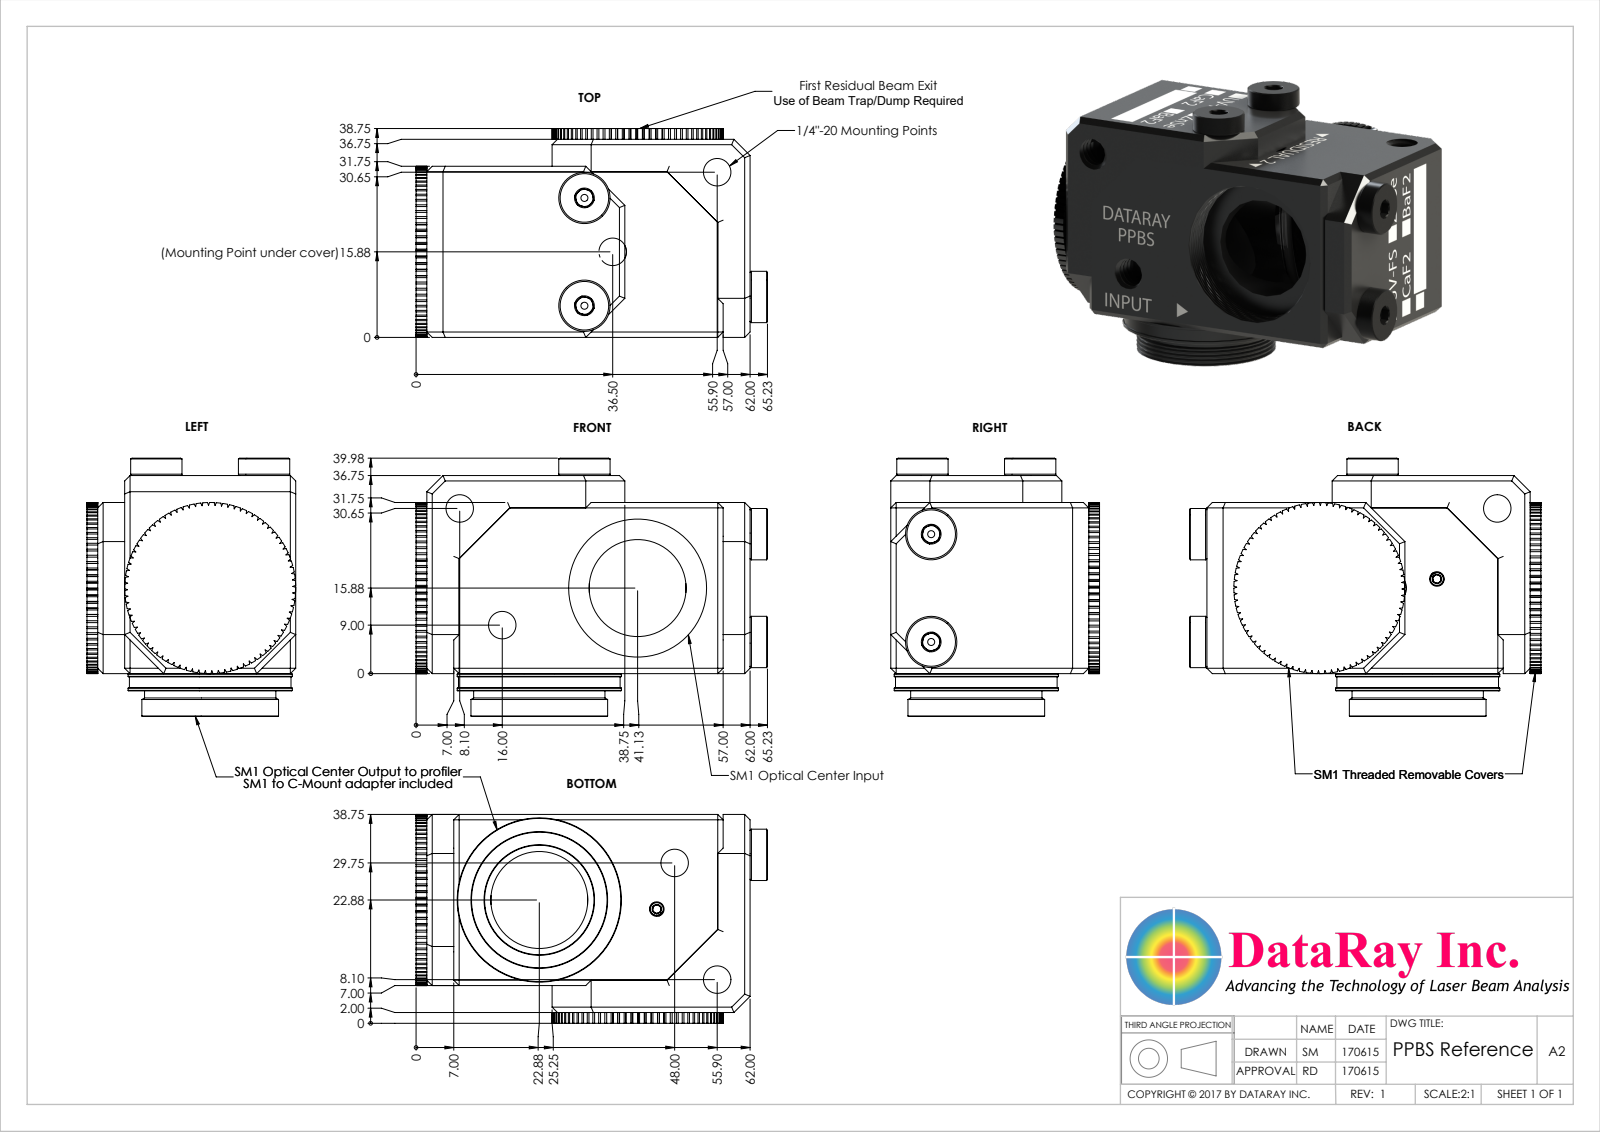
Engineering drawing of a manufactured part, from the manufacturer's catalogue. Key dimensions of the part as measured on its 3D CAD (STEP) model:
Part name (STEP PRODUCT): Adapter-CM(M)-SM1(M); Cap-PPBS; Mount Fastener; Wedge-UV-FS (+4 more)
STEP written by: SolidWorks 2017 (CONFIG_CONTROL_DESIGN)
Units: millimetres
Bodies: 14 solids, 1243 faces (544 planar, 441 cylindrical, 258 other)
Overall size (bounding box): 65.23 × 47.93 × 38.75
Volume: 52 327 mm³ · Surface area: 32 496 mm²
Round holes (diameter × count): ⌀5.11 ×10, ⌀25.4 ×4, ⌀18 ×3, ⌀2.71 ×2, ⌀6.35 ×2, ⌀20 ×2, ⌀25.6 ×2, ⌀20.32 ×1
Round bosses / shafts (diameter × count): ⌀5.39 ×28, ⌀9.52 ×4, ⌀6.35 ×4, ⌀26.29 ×2, ⌀3 ×2, ⌀1.6 ×2, ⌀30.48 ×1, ⌀30 ×1
Partial cylindrical surfaces — rounded edges, fillets, slot ends (radius × count): R2.69 ×4, R15.88 ×2
Main face-to-face distances: 5, 31.75, 2, 7, 57, 3, 55, 31.76, 36.75, 33.75
Hole centre spacings: 13.05, 13.04, 20, 26.05, 8.36, 9.19, 11.29, 13.4
